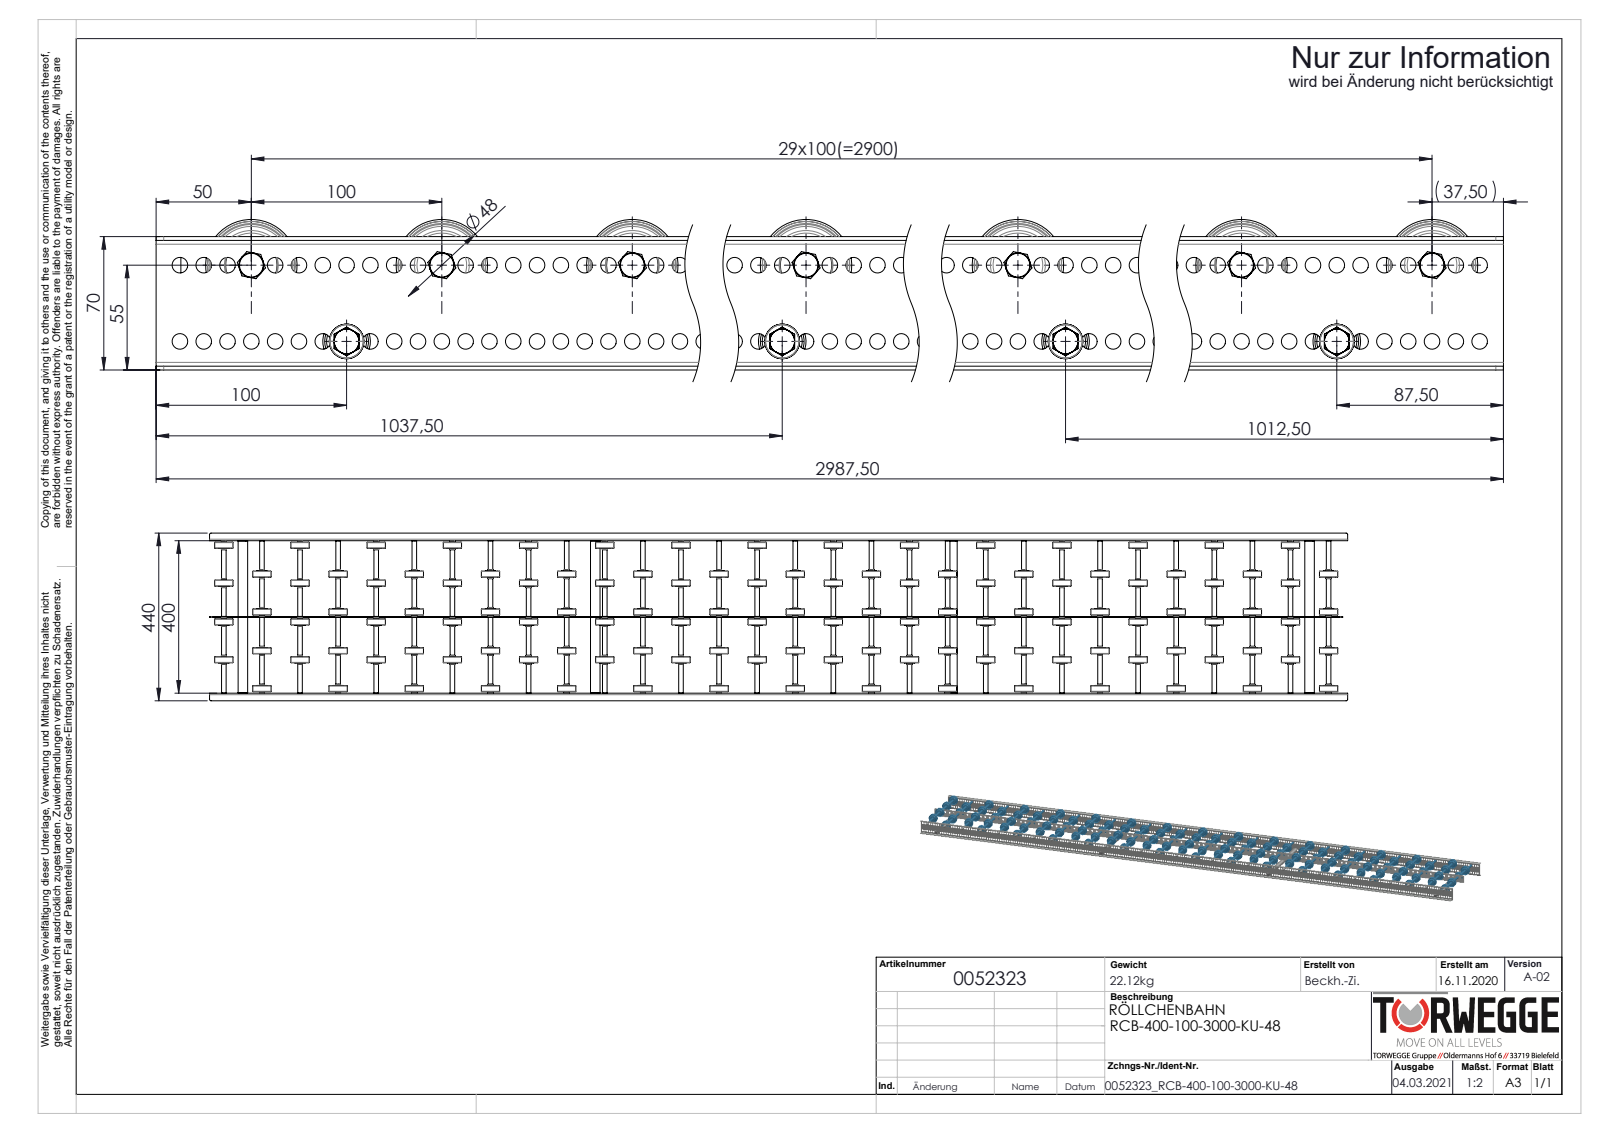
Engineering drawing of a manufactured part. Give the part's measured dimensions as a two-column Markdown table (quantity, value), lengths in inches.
| quantity | value |
| --- | --- |
| part name | 0046278_KB-ROHR-12X1,75mm_KFG_L75,5; S100994_Sperrzahnschraube_M08x16-8.8-A2K; Hutmutter_DIN_1587_M8; 0011532_2300-48-8 (+6 more) |
| STEP written by | SolidWorks 2020 (AUTOMOTIVE_DESIGN) |
| units | inches |
| bodies | 353 solids, 13580 faces (2310 planar, 5182 cylindrical, 6088 other) |
| overall size | 117.618 × 17.323 × 3.11 |
| volume | 308.7 in³ |
| surface area | 6 006 in² |
| round holes (diameter × count) | 0.323 × 476, 0.335 × 119, 0.262 × 30, 0.38 × 30, 0.539 × 30, 0.268 × 4, 0.827 × 4 |
| round bosses / shafts (diameter × count) | 0.315 × 34, 1.89 × 30, 1.063 × 30, 0.5 × 30, 0.492 × 30, 0.472 × 30, 0.984 × 4 |
| partial cylindrical surfaces (radius × count) | 0.157 × 8, 0.079 × 4, 0.197 × 4 |
| main face-to-face distances | 0.079, 15.827, 2.677, 15.748, 15.906, 7.917, 7.819, 7.909, 7.831, 7.996 |
| hole center spacings | 0.492, 0.984, 1.476, 1.969, 2.461, 2.953, 3.445, 3.937 |
